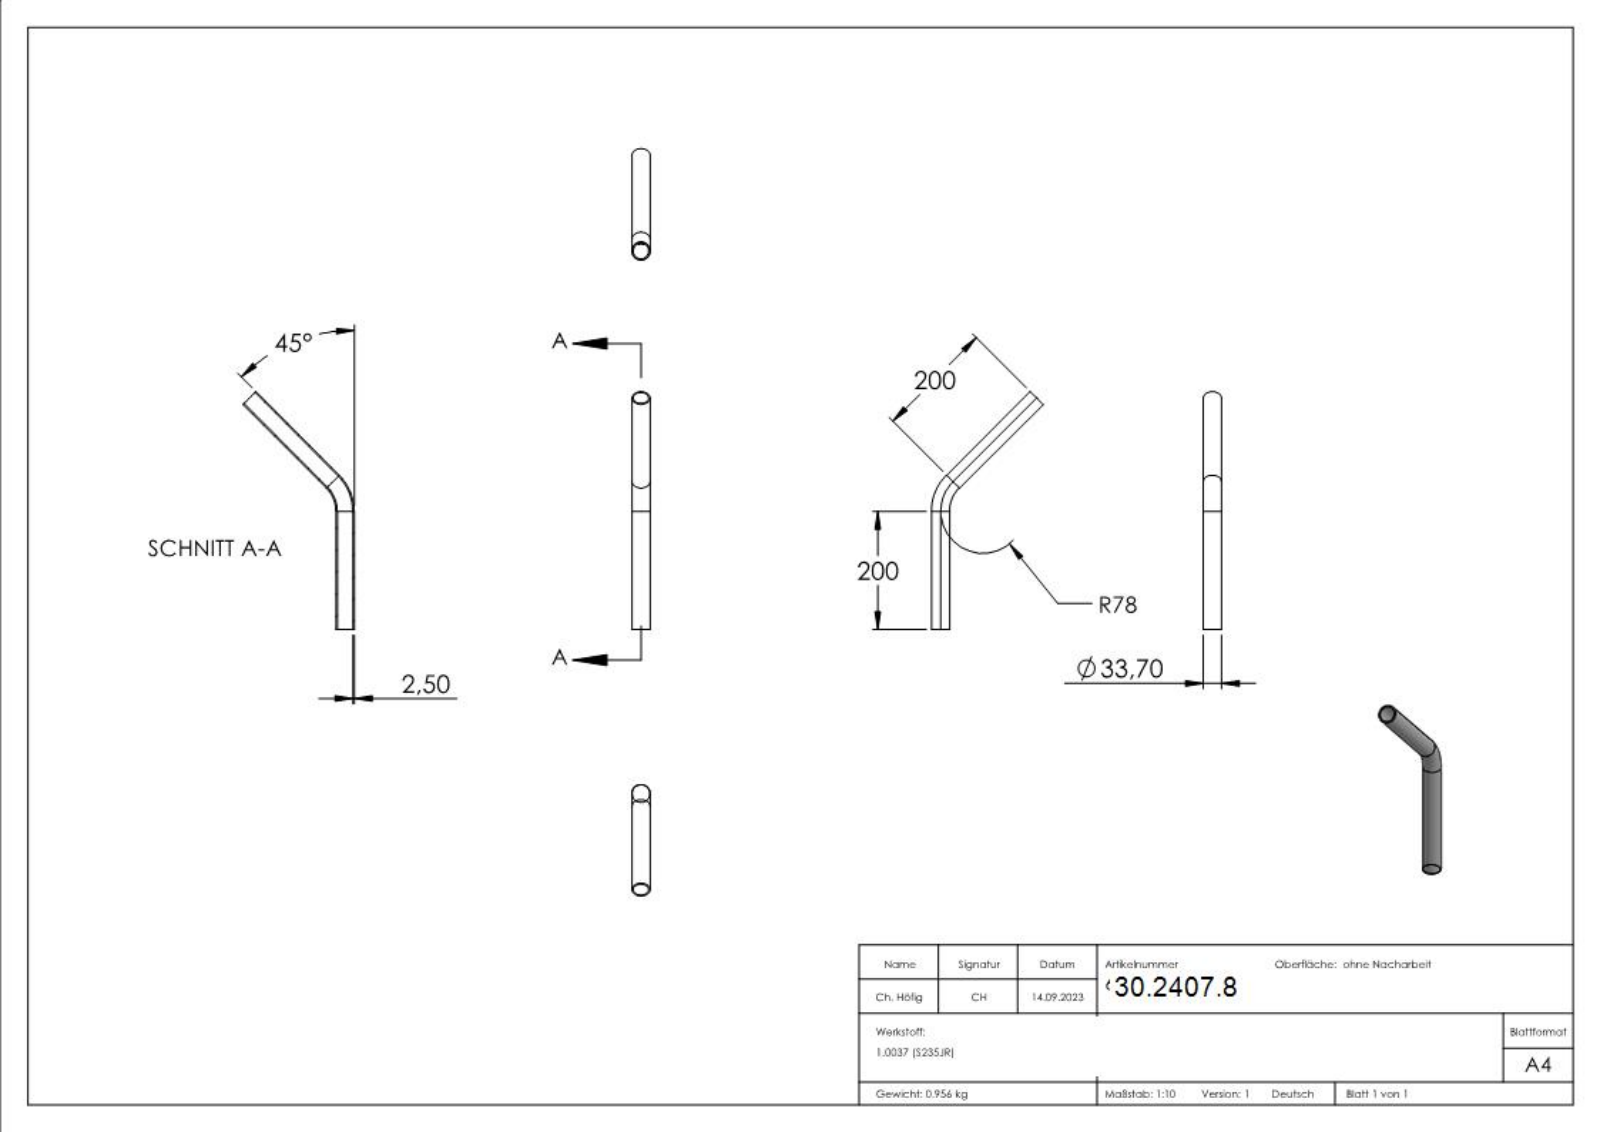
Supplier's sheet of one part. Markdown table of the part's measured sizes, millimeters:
| quantity | value |
| --- | --- |
| part name | 6966-045 |
| STEP written by | SolidWorks 2018 (CONFIG_CONTROL_DESIGN) |
| units | millimeters |
| bodies | 1 solid, 223 faces (116 planar, 4 cylindrical, 103 other) |
| overall size | 441.56 × 206.73 × 33.7 |
| volume | 122 522 mm³ |
| surface area | 98 511 mm² |
| round holes (diameter × count) | 28.7 × 2 |
| round bosses / shafts (diameter × count) | 33.7 × 2 |
| main face-to-face distances | 0.34, 0.53, 0.58, 0.31, 0.39, 0.32, 0.48, 0.54, 0.35, 0.52 |
